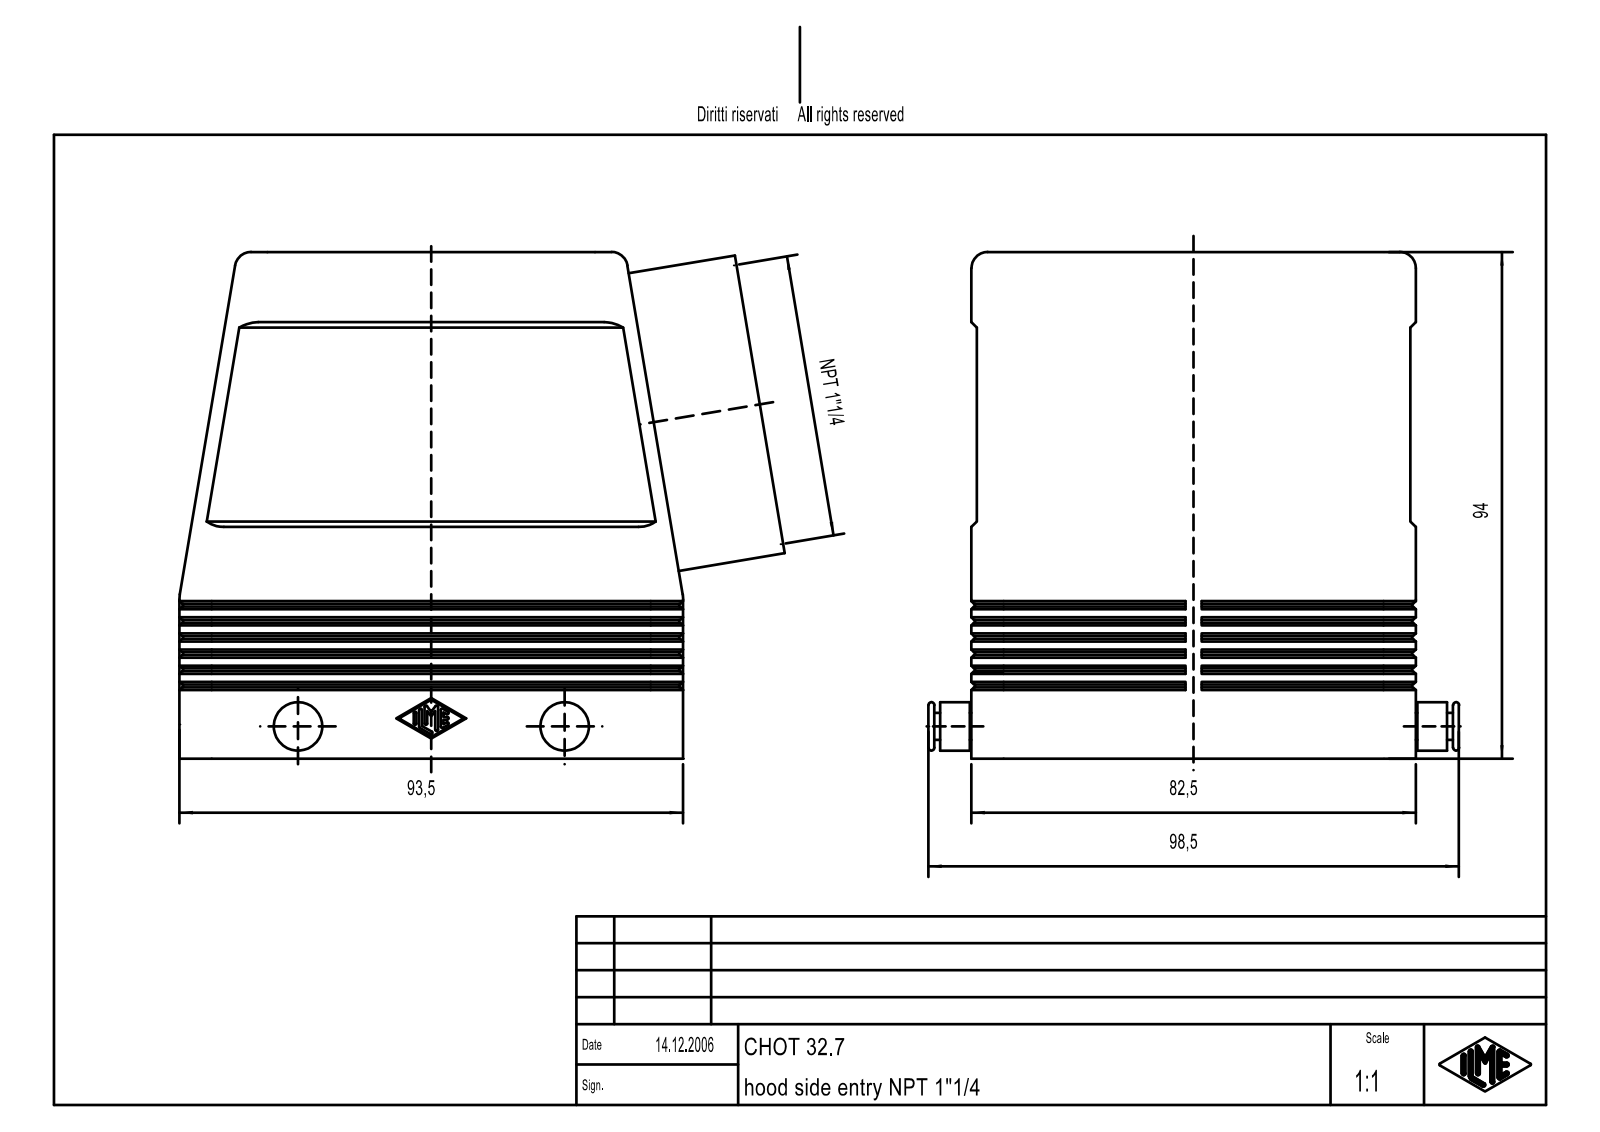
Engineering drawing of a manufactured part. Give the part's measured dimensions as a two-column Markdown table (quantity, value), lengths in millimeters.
| quantity | value |
| --- | --- |
| part name | MSBO10379 |
| STEP written by | Creo Elements/Direct Modeling 18.0B 02-Dec-2011 (C) Parametric Technology GmbH (AUTOMOTIVE_DESIGN) |
| units | millimeters |
| bodies | 1 solid, 525 faces (277 planar, 150 cylindrical, 98 other) |
| overall size | 112.36 × 98.5 × 94 |
| volume | 171 623 mm³ |
| surface area | 80 248 mm² |
| round holes (diameter × count) | 3.5 × 8, 2.46 × 6, 2.46 × 2 |
| round bosses / shafts (diameter × count) | 9 × 2, 5 × 2, 56 × 1 |
| partial cylindrical surfaces (radius × count) | 0.25 × 14, 2 × 12, 6 × 10, 3 × 4, 5.3 × 4, 27.08 × 1, 28 × 1 |
| main face-to-face distances | 4, 78.5, 74.5, 82.5, 3, 1, 81.5, 77.5, 71.5, 11 |
| hole center spacings | 27, 35, 77.5, 82.07, 85.04, 8, 62, 77.91 |
